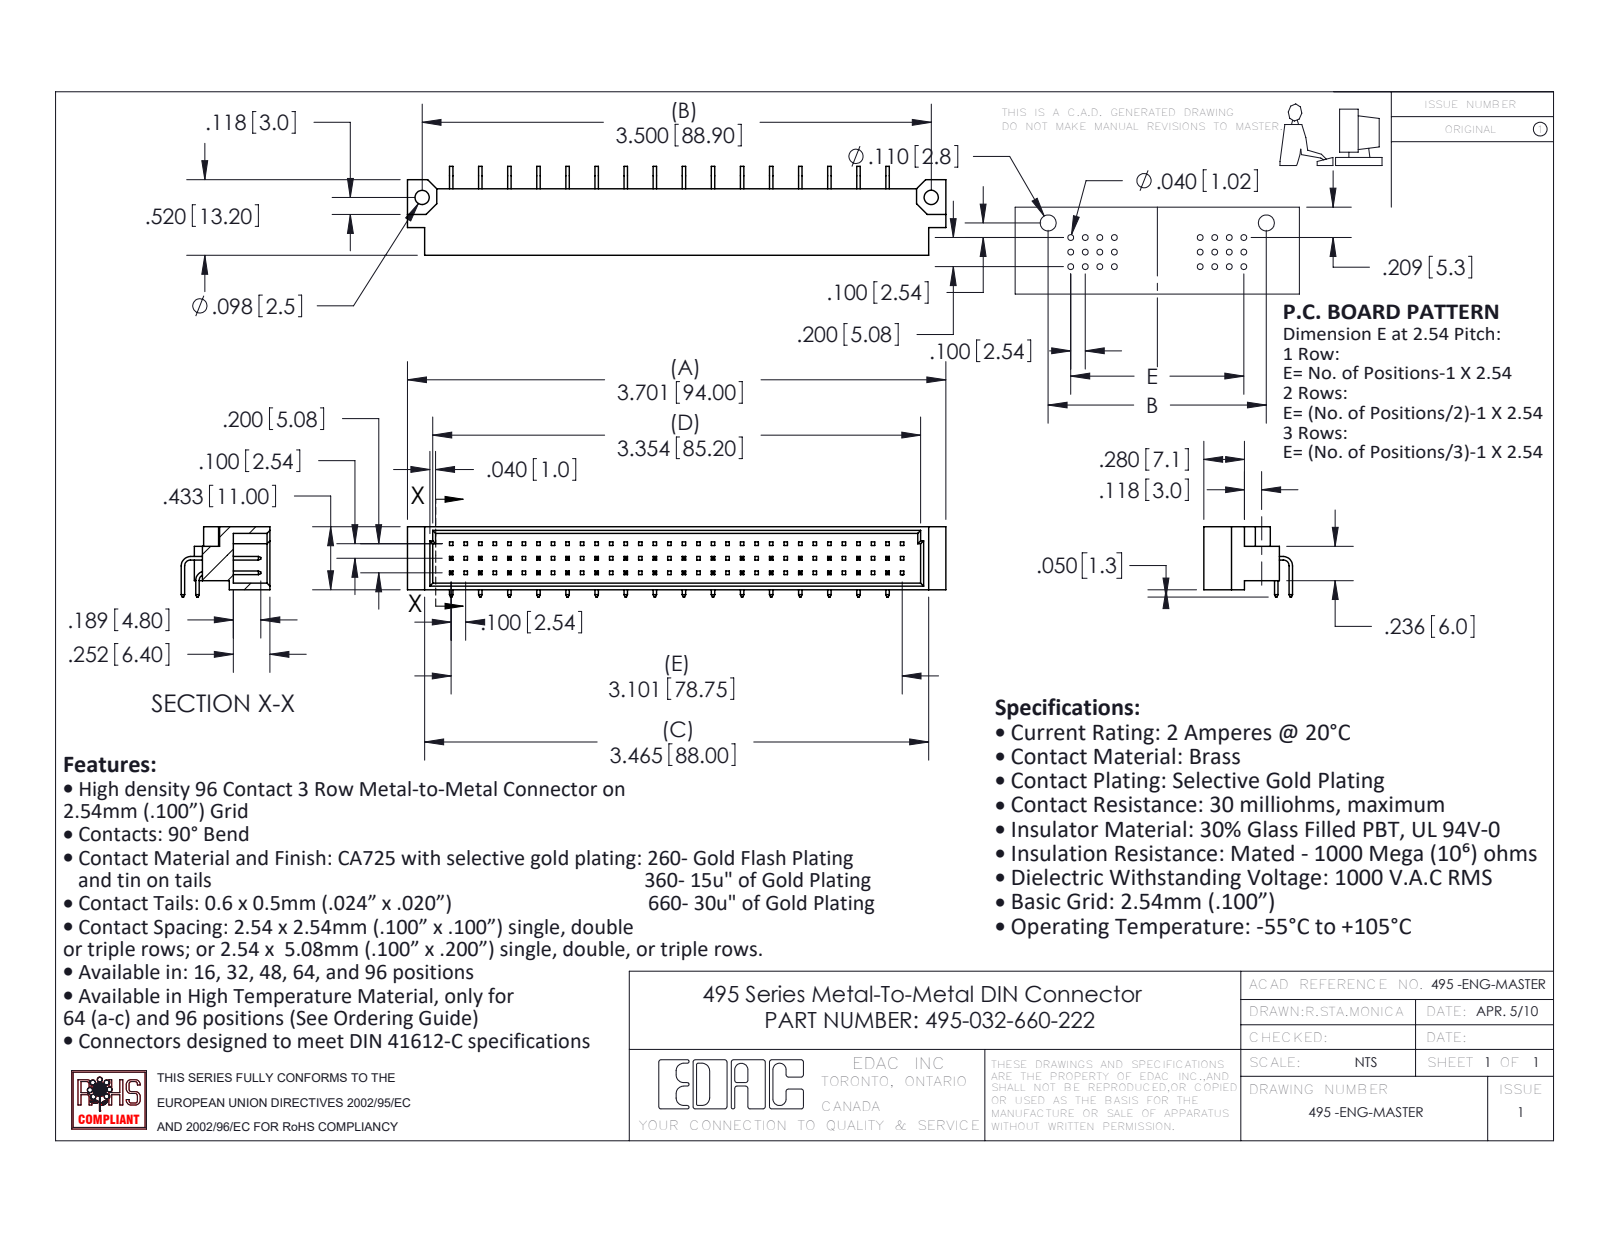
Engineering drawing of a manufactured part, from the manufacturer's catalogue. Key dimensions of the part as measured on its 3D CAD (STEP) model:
Part name (STEP PRODUCT): 495-290-3; 495-032-660-222; 495 Part_96; 495-290-2
STEP written by: SolidWorks 2020 (AUTOMOTIVE_DESIGN)
Units: millimetres
Bodies: 33 solids, 1009 faces (941 planar, 68 cylindrical, 0 other)
Overall size (bounding box): 94 × 15.51 × 12.27
Volume: 6 130 mm³ · Surface area: 8 180 mm²
Round holes (diameter × count): ⌀2.49 ×2
Partial cylindrical surfaces — rounded edges, fillets, slot ends (radius × count): R1.02 ×2, R1.65 ×2
Main face-to-face distances: 1.14, 9.86, 5.2, 11, 2.54, 0.61, 5.08, 8.72, 1.6, 9.4
Hole centre spacings: 88.9
